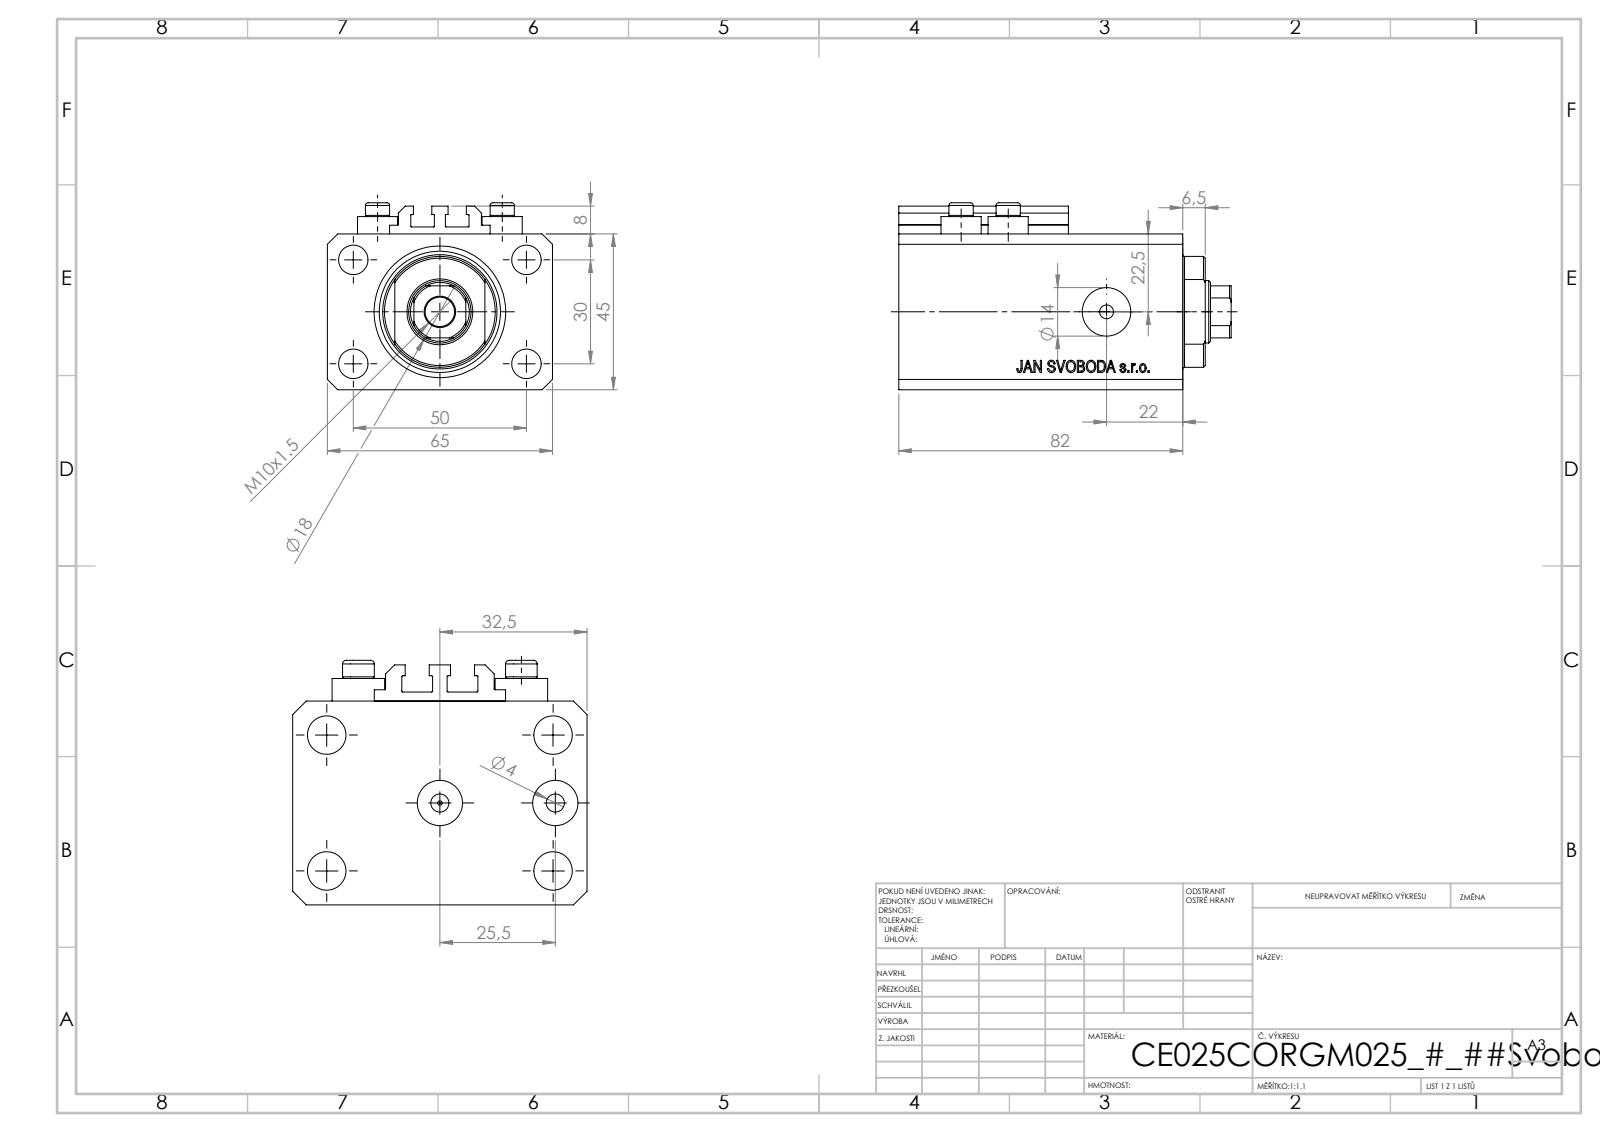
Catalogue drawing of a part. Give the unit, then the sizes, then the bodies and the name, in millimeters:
Units: millimetres
Overall size (bounding box): 96 × 65 × 54
Round holes (diameter × count): ⌀4 ×8, ⌀8.5 ×5, ⌀10 ×2, ⌀14 ×2, ⌀1.25 ×1, ⌀18 ×1, ⌀25 ×1, ⌀38 ×1
Round bosses / shafts (diameter × count): ⌀11.6 ×4, ⌀7 ×4
Partial cylindrical surfaces — rounded edges, fillets, slot ends (radius × count): R0.2 ×10, R8.5 ×1, R16 ×1
Main face-to-face distances: 45, 65, 14, 82, 68, 47, 6.9, 61.1, 75.1, 3
Hole centre spacings: 29.15, 13.6, 15.01, 30, 36, 38.48, 50, 52.68
Volume: 224 350 mm³ · Surface area: 60 459 mm²
Bodies: 8 solids, 1042 faces (504 planar, 92 cylindrical, 446 other)
Part name (STEP PRODUCT): V250CE_C_VCP; ALLEN BOLT V250CE; V250CE_VC_C; V250CE_C_Body
STEP written by: SolidWorks 2019 (CONFIG_CONTROL_DESIGN)
